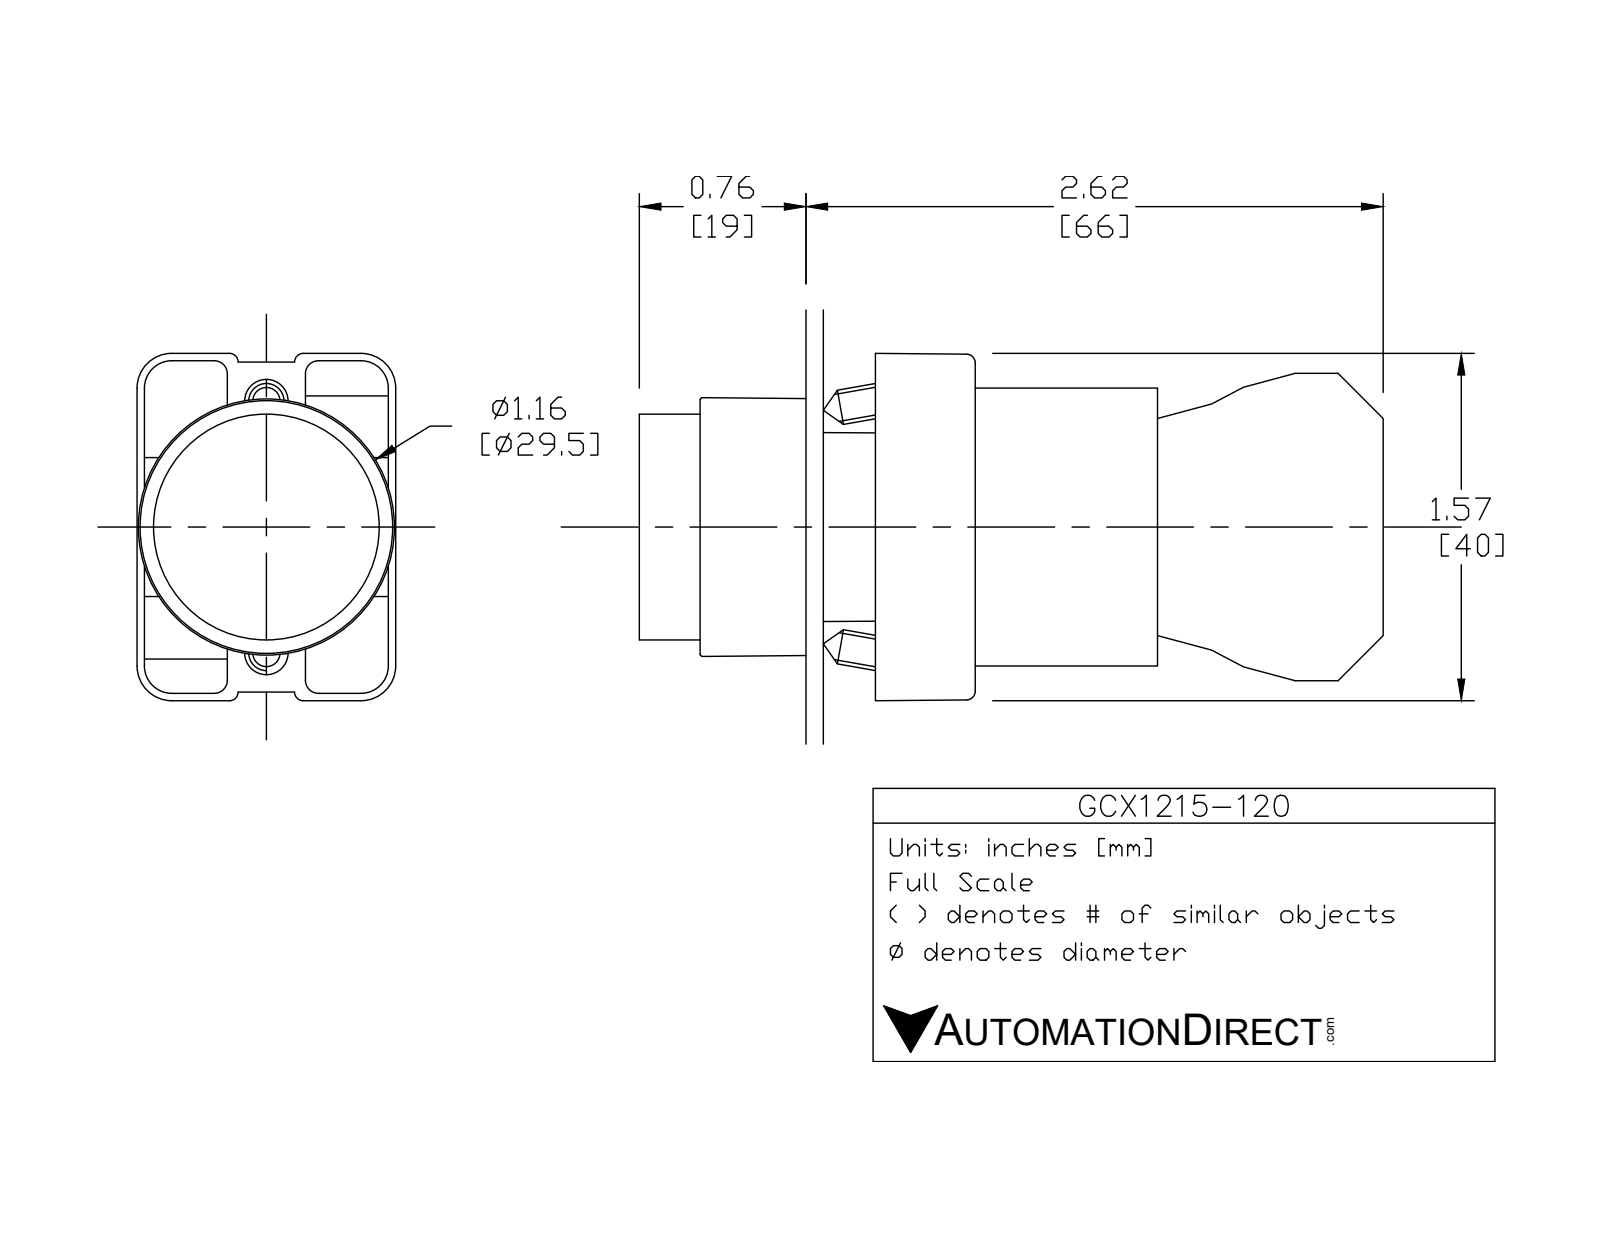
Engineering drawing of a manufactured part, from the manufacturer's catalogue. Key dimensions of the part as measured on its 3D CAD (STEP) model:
Part name (STEP PRODUCT): GCX1215 OPERATOR; ECX1050; ecx1040; GCX1215-120 (+1 more)
STEP written by: SolidWorks 2016 (AUTOMOTIVE_DESIGN)
Units: inches
Bodies: 7 solids, 425 faces (250 planar, 144 cylindrical, 31 other)
Overall size (bounding box): 3.319 × 1.581 × 1.177
Volume: 2.721 in³ · Surface area: 36.32 in²
Round holes (diameter × count): ⌀0.079 ×2, ⌀0.124 ×2, ⌀0.13 ×2, ⌀0.087 ×1, ⌀0.197 ×1, ⌀0.469 ×1, ⌀0.878 ×1, ⌀0.888 ×1, ⌀1.024 ×1
Round bosses / shafts (diameter × count): ⌀0.157 ×4, ⌀1.175 ×1, ⌀1.004 ×1, ⌀0.945 ×1, ⌀0.856 ×1, ⌀0.78 ×1, ⌀0.504 ×1
Partial cylindrical surfaces — rounded edges, fillets, slot ends (radius × count): R0.059 ×24, R0.041 ×12, R0.124 ×12, R0.157 ×12, R0.039 ×8, R0.128 ×2, R0.02 ×1, R0.063 ×1
Main face-to-face distances: 0.827, 0.579, 1.171, 2.02, 1.193, 0.031, 0.033, 0.573, 1.165, 0.593
Hole centre spacings: 0.236, 0.544, 0.472, 0.49
